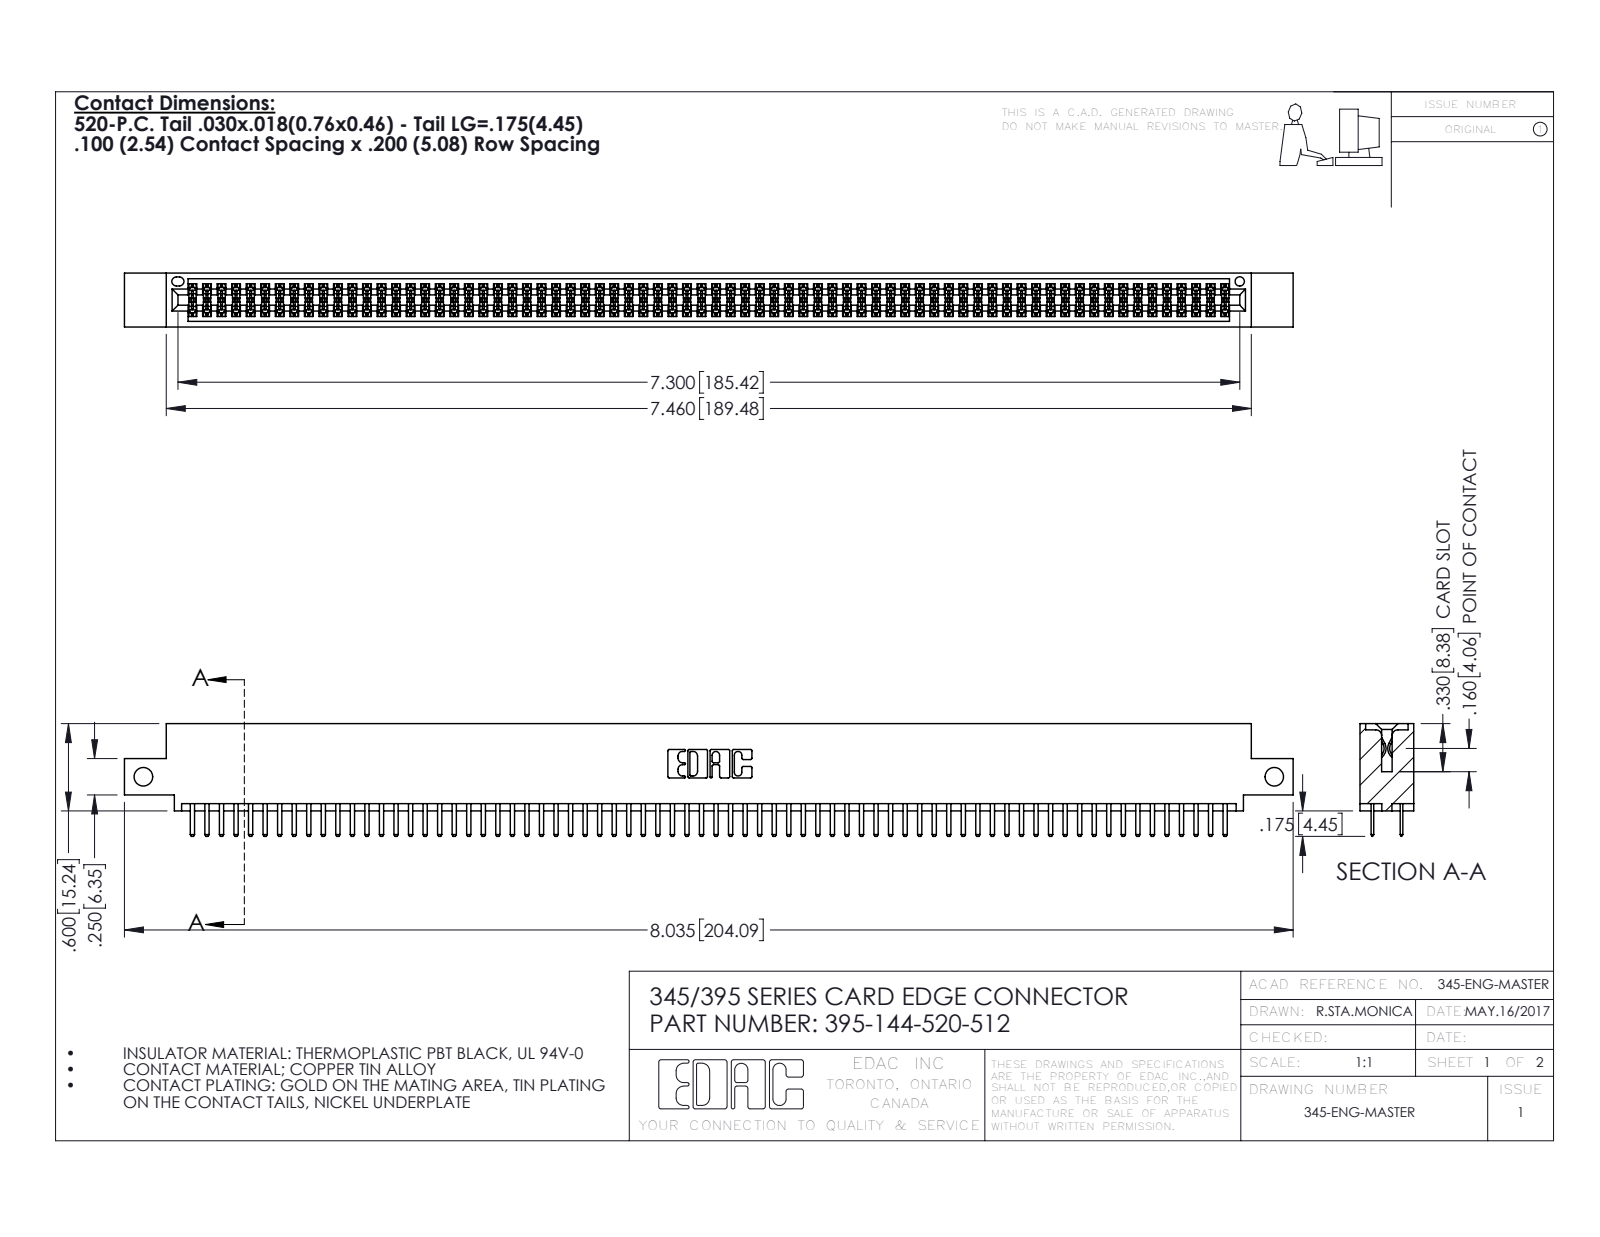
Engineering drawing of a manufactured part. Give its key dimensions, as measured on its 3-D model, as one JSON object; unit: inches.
{"part_name": "345-292-001_345-293-120; 395-144-520-512; 345 Part_0.110 Offset - Side Mount", "step_written_by": "SolidWorks 2016 (CONFIG_CONTROL_DESIGN)", "units": "inches", "bodies": {"solids": 145, "faces": 7906, "planar": 5124, "cylindrical": 2782, "other": 0}, "overall_size": [8.035, 0.775, 0.37], "volume_in3": 1.213, "surface_area_in2": 46.17, "round_holes": [[0.128, 2], [0.064, 1]], "partial_cylinders_radius": [[0.006, 216], [0.01, 148], [0.01, 22], [0.007, 6], [0.031, 6], [0.026, 3], [0.014, 2], [0.019, 2]], "face_to_face_distances": [0.072, 0.298, 0.2, 0.37, 0.098, 0.272, 0.025, 0.225, 0.022, 0.072], "hole_center_spacings": [7.775]}
